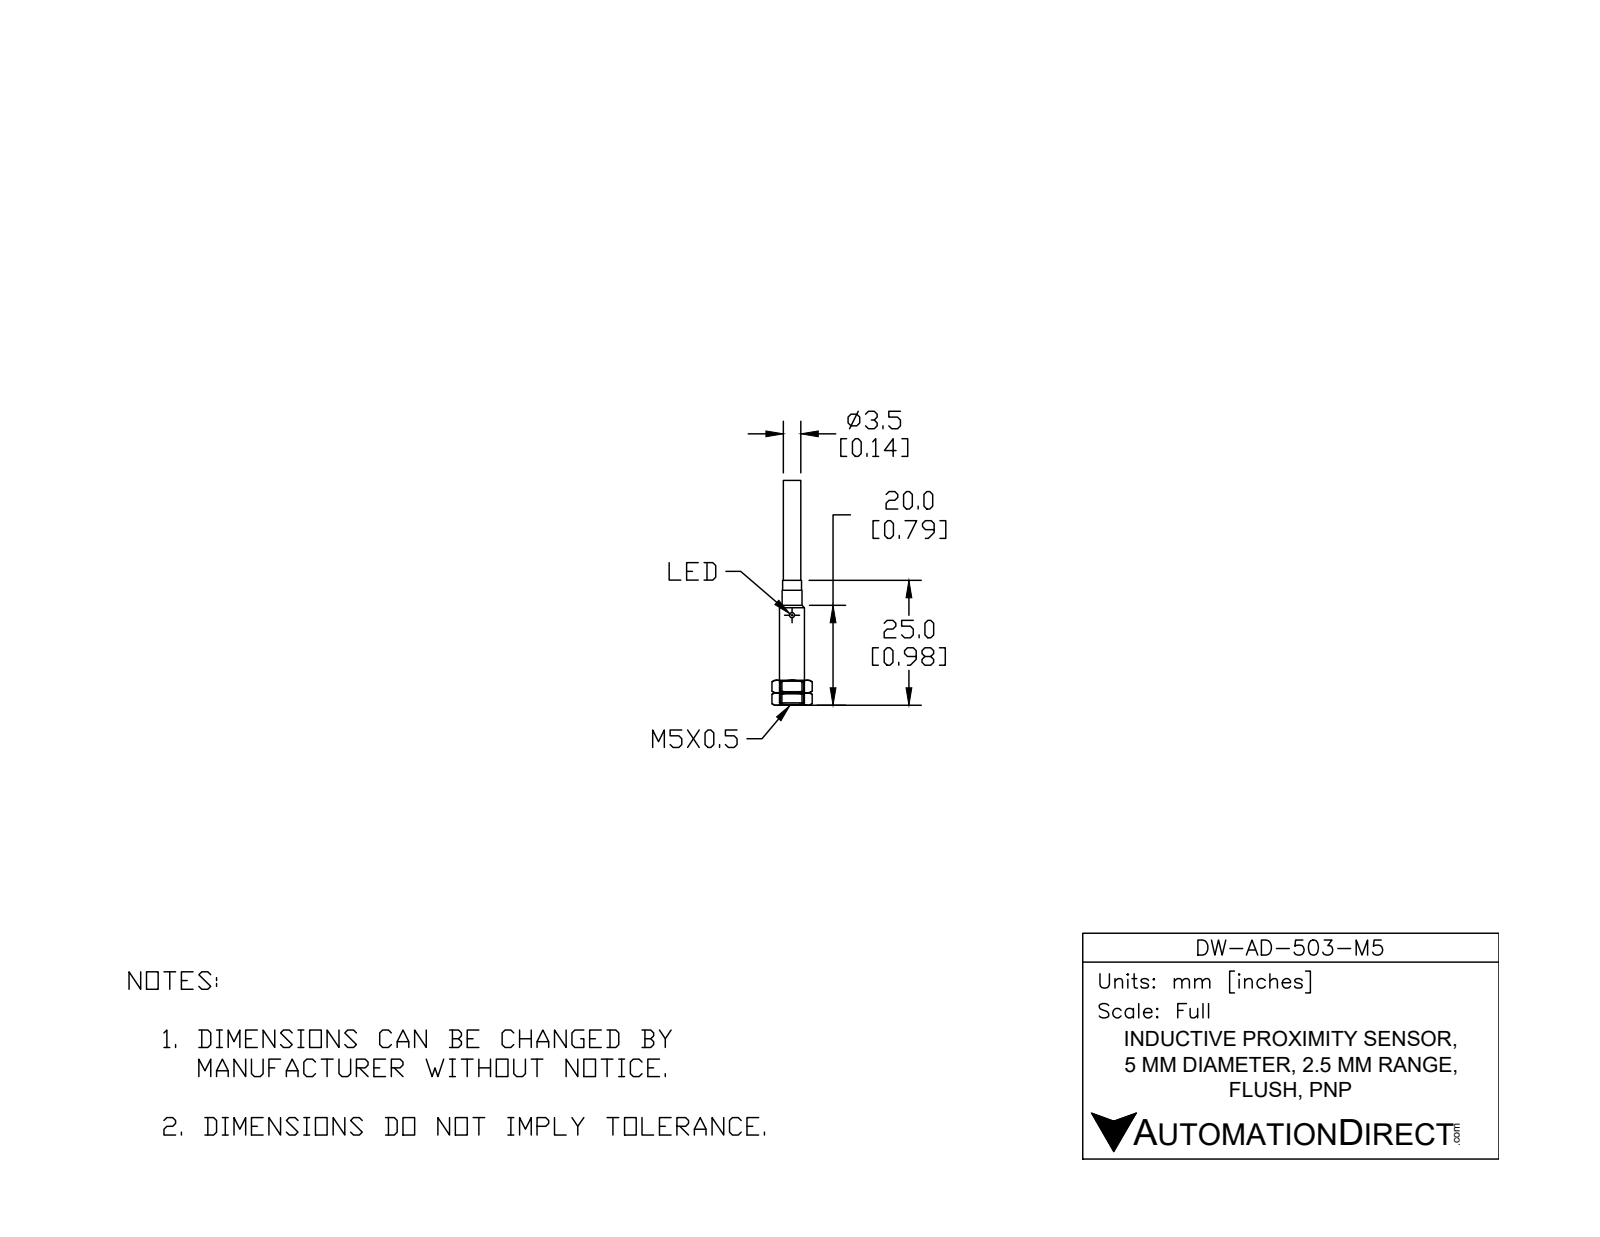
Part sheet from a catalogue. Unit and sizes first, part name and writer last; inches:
Units: inches
Overall size (bounding box): 1.887 × 0.197 × 0.197
Round holes (diameter × count): ⌀0.059 ×1, ⌀0.14 ×1
Round bosses / shafts (diameter × count): ⌀0.197 ×1, ⌀0.165 ×1, ⌀0.138 ×1
Main face-to-face distances: 0.03, 0.787, 0.757, 0.984, 0.954, 0.197
Volume: 0.029 in³ · Surface area: 1.554 in²
Bodies: 2 solids, 14 faces (4 planar, 6 cylindrical, 4 other)
Part name (STEP PRODUCT): DW-AD-503-M5
STEP written by: SolidWorks 2017 (AUTOMOTIVE_DESIGN)
